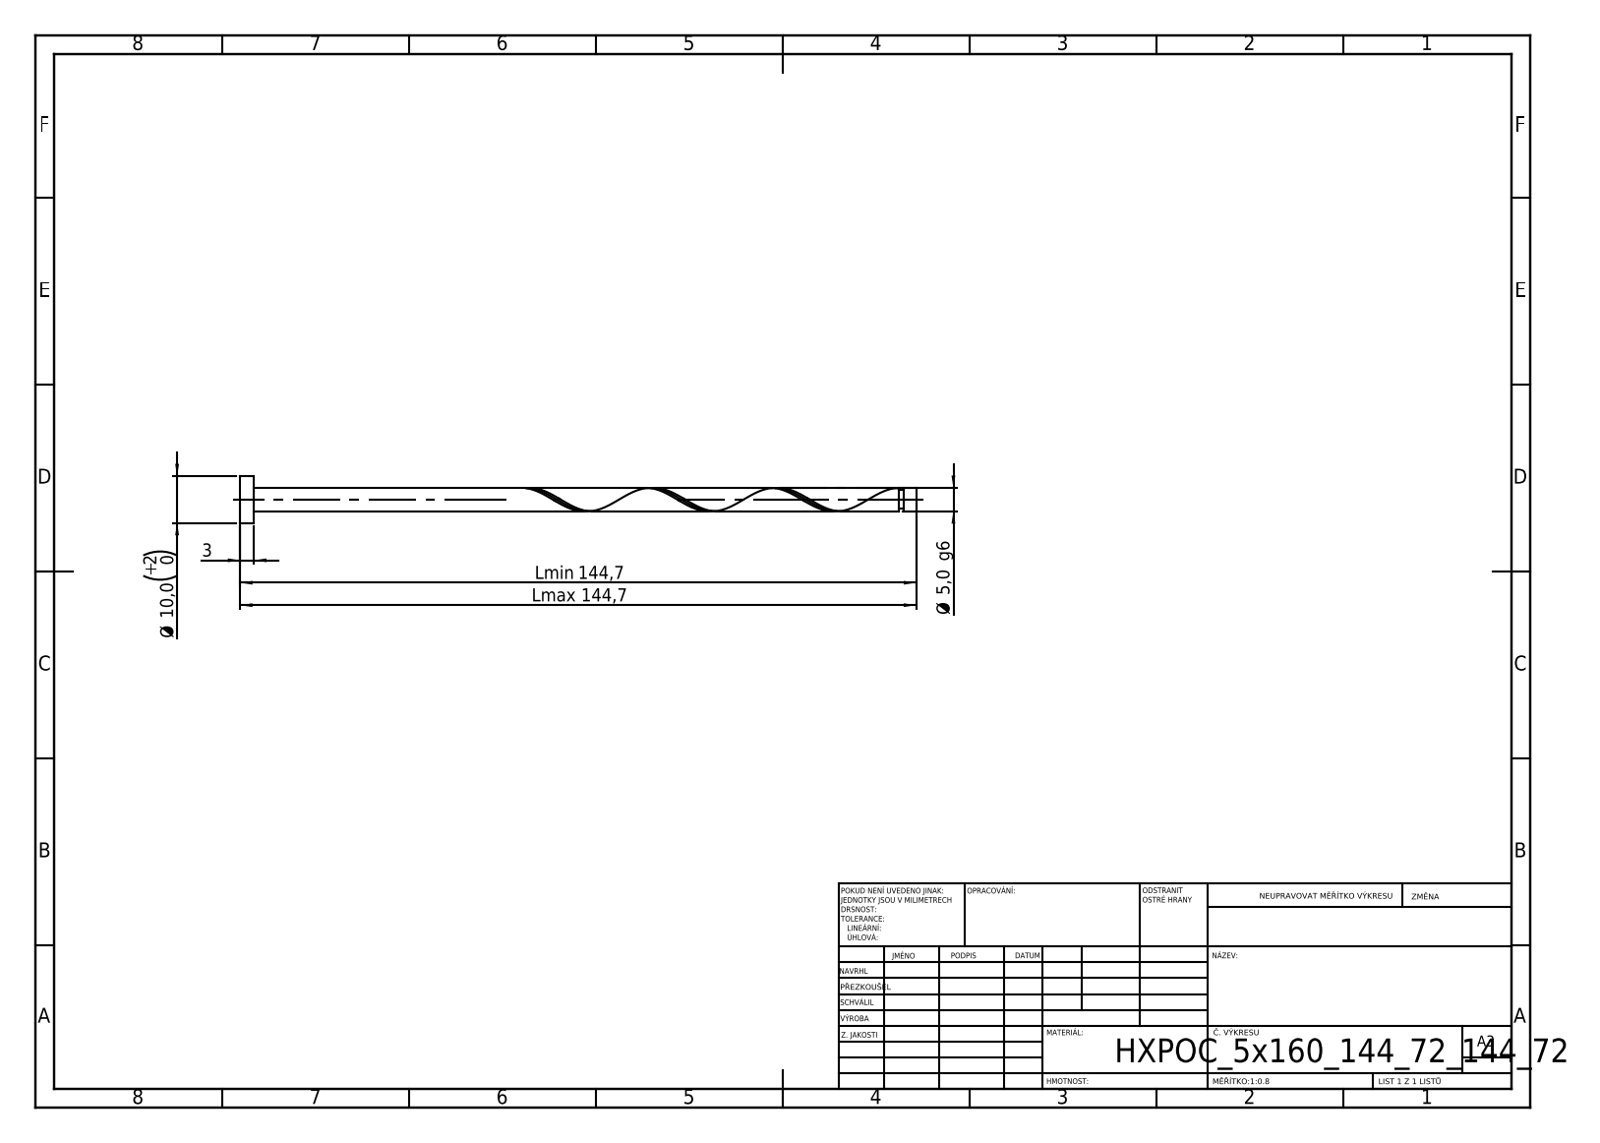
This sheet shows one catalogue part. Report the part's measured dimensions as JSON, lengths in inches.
{"step_written_by": "SolidWorks 2019 (CONFIG_CONTROL_DESIGN)", "units": "inches", "bodies": {"solids": 1, "faces": 21, "planar": 6, "cylindrical": 14, "other": 1}, "overall_size": [5.698, 0.394, 0.394], "volume_in3": 0.182, "surface_area_in2": 3.929, "round_bosses_or_shafts": [[0.394, 1], [0.197, 1], [0.157, 1]], "face_to_face_distances": [0.118, 5.698, 5.58, 5.595, 5.477, 0.102, 5.556, 5.438, 0.039, 0.142]}
